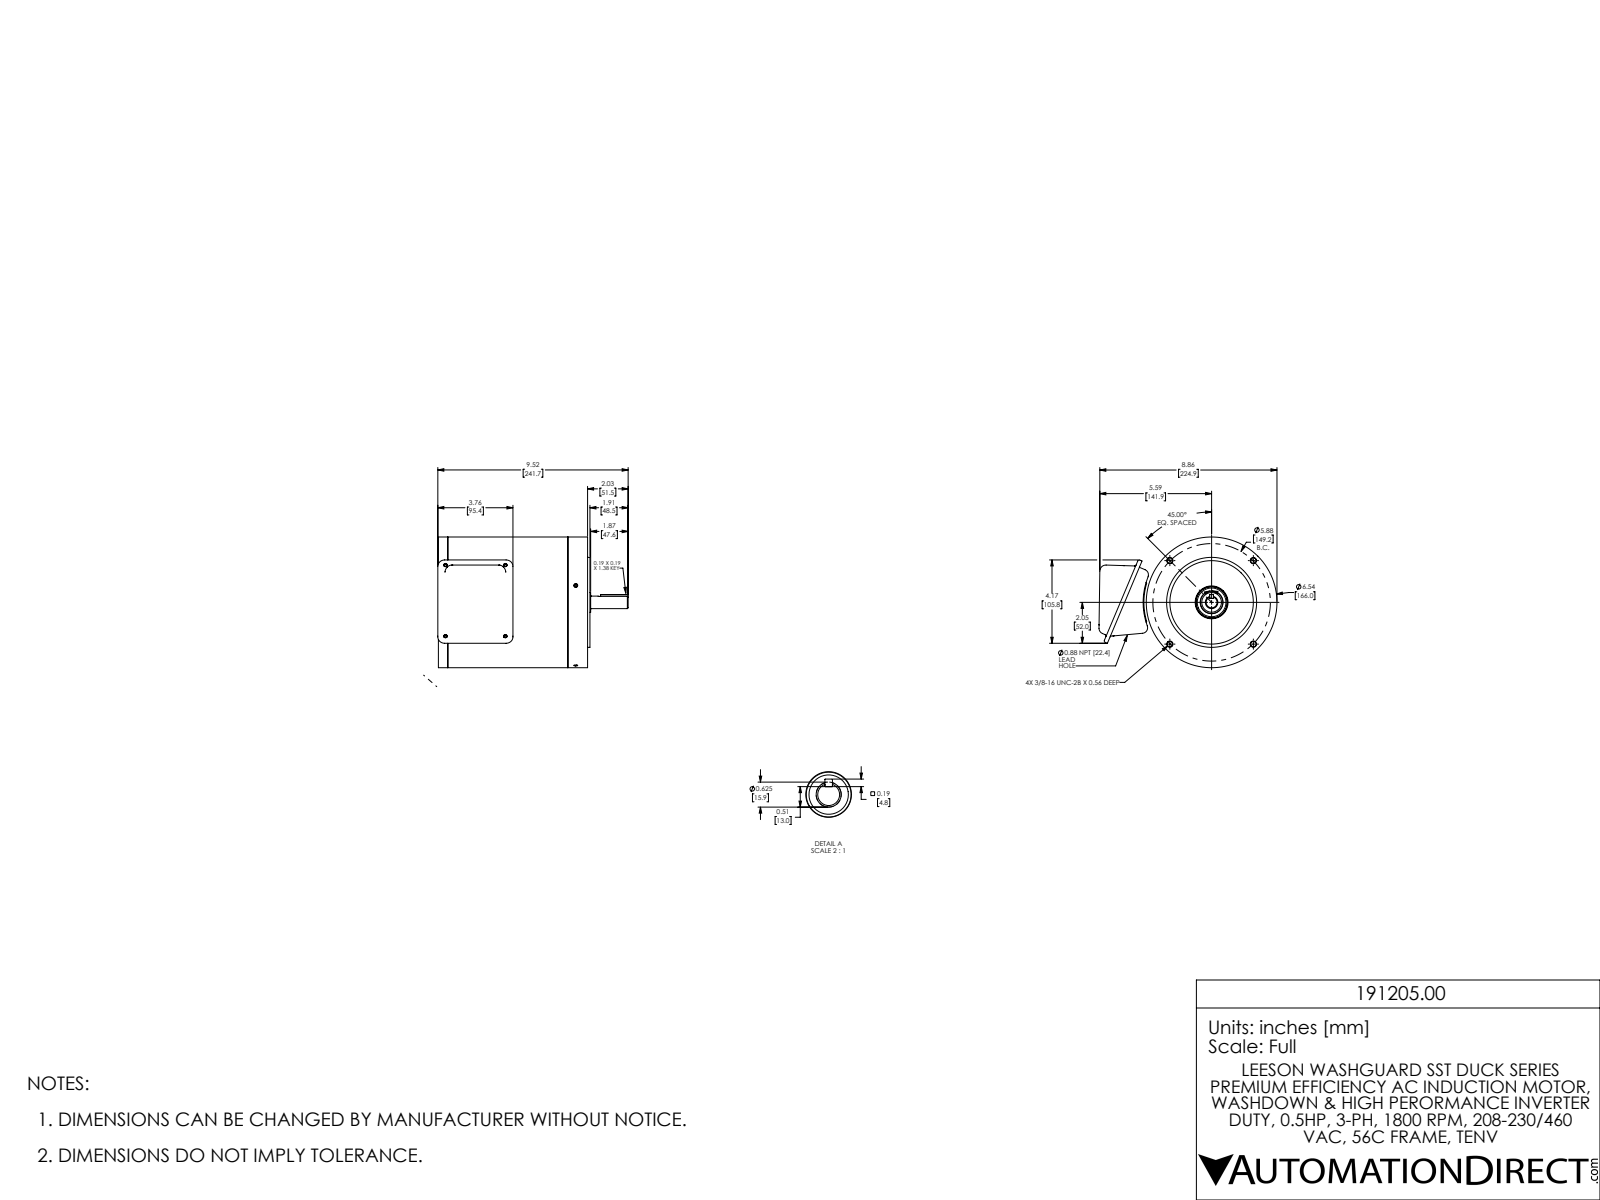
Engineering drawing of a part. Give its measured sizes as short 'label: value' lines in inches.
name: 191202
written by: SolidWorks 2017 (AUTOMOTIVE_DESIGN)
unit: in
bodies: 9 solids, 645 faces (104 planar, 250 cylindrical, 291 other)
size: 9.516 × 8.898 × 6.535
volume: 42.46 in³; area: 622 in²
holes: 9× ⌀0.13, 8× ⌀0.165, 8× ⌀0.268, 4× ⌀0.177, 4× ⌀0.228, 2× ⌀0.118, 2× ⌀0.197, 1× ⌀0.189, 1× ⌀0.866, 1× ⌀0.984, 1× ⌀1.26, 1× ⌀1.378
bosses: 1× ⌀6.535, 1× ⌀4.5, 1× ⌀1.575, 1× ⌀1.22, 1× ⌀1.181, 1× ⌀1.122, 1× ⌀0.986, 1× ⌀0.976
rounds: 20× R0.079, 9× R0.236, 9× R0.276, 9× R0.303, 8× R0.039, 8× R0.157, 6× R0.02, 6× R0.098
face distances: 0.039, 0.217, 0.197, 7.461, 7.244, 0.236, 0.394, 7.224, 0.118, 7.047
hole spacings: 2.231, 2.953, 5.383, 2.992, 0.515, 1.754, 2.203, 2.691
